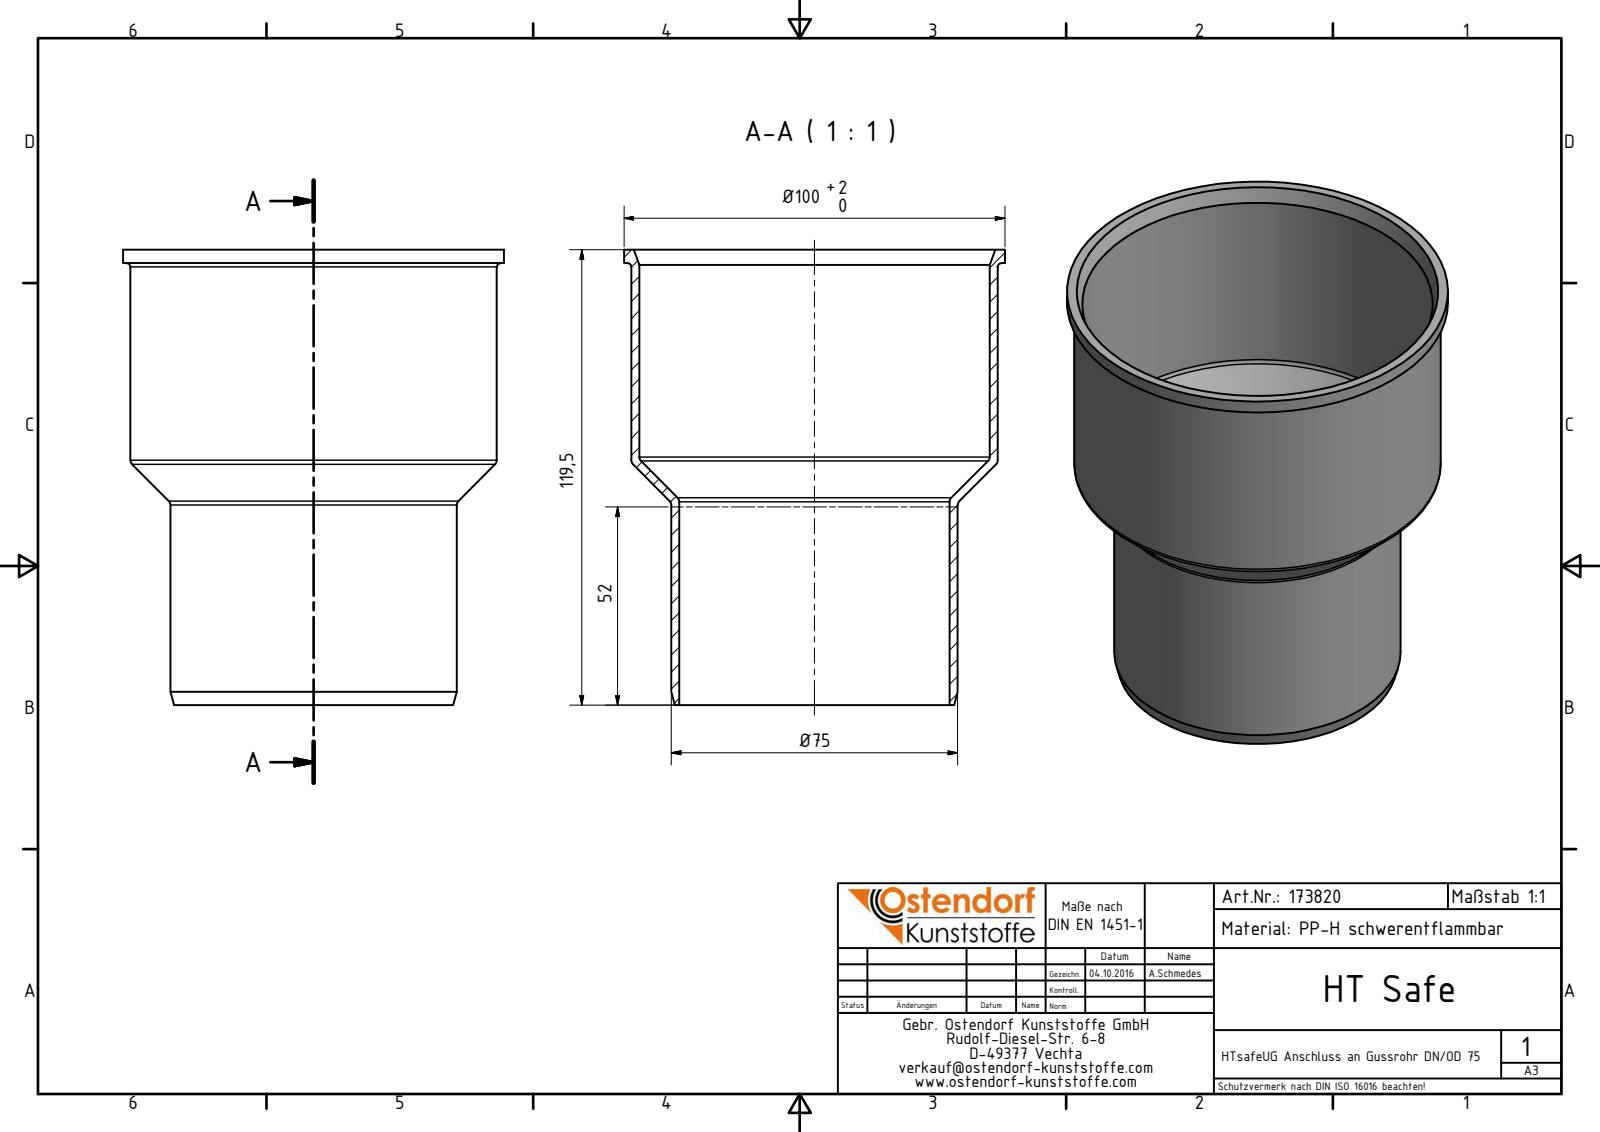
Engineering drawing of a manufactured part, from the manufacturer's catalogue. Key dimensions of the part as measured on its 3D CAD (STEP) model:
Part name (STEP PRODUCT): 173820 HTsafeUG DN_OD 75
STEP written by: Autodesk Inventor 2016 (AUTOMOTIVE_DESIGN)
Units: millimetres
Bodies: 1 solid, 17 faces (3 planar, 5 cylindrical, 9 other)
Overall size (bounding box): 119.5 × 100 × 100
Volume: 69 317 mm³ · Surface area: 66 763 mm²
Round holes (diameter × count): ⌀71 ×1, ⌀92 ×1
Round bosses / shafts (diameter × count): ⌀100 ×1, ⌀96.2 ×1, ⌀75.2 ×1
Main face-to-face distances: 3.5, 116, 119.5
